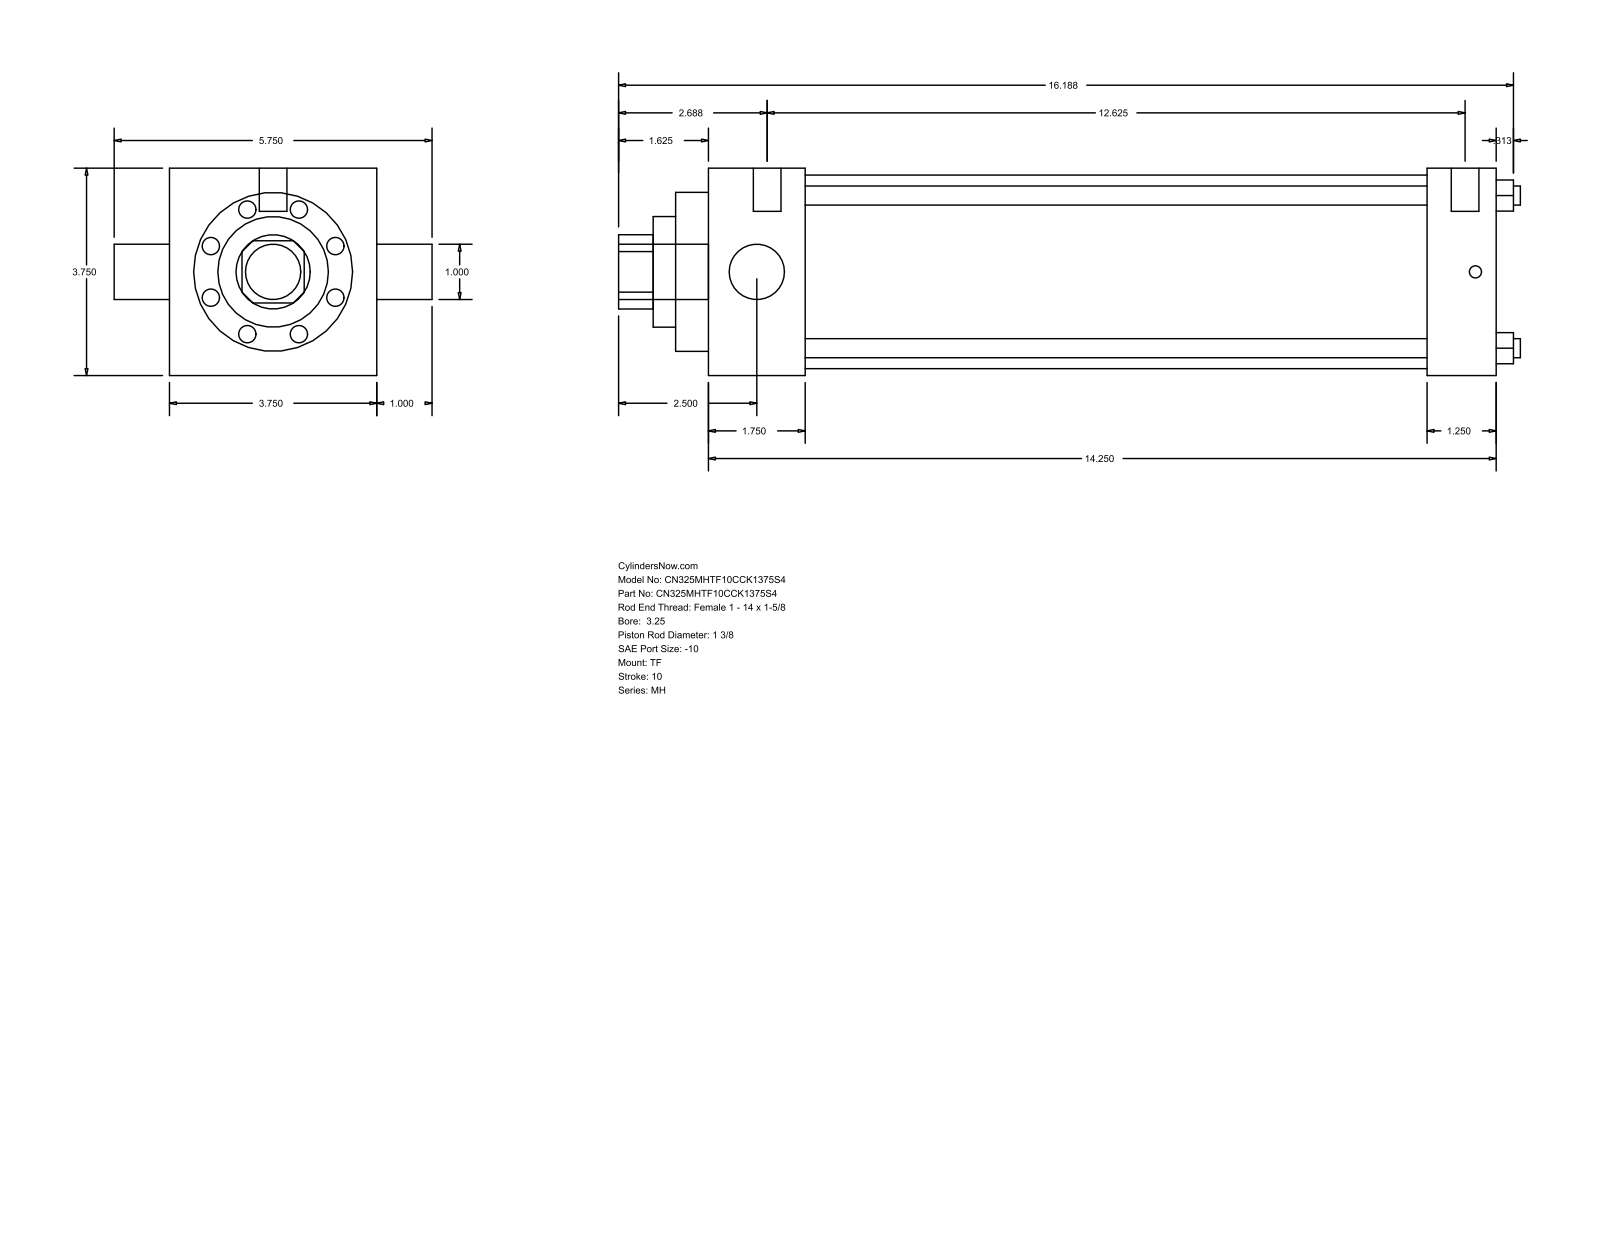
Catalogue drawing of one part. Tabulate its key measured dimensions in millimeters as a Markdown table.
| quantity | value |
| --- | --- |
| part name | MH_TF__0325_1.375 |
| STEP written by | GSSL Pune (CONFIG_CONTROL_DESIGN) |
| units | millimeters |
| bodies | 0 solids, 86 faces (61 planar, 25 cylindrical, 0 other) |
| overall size | 414.34 × 146.05 × 95.25 |
| round holes (diameter × count) | 8.76 × 4, 25.4 × 1, 34.92 × 1, 50.8 × 1, 73.03 × 1, 88.9 × 1 |
| round bosses / shafts (diameter × count) | 5.56 × 3, 12.7 × 2, 25.4 × 1 |
| partial cylindrical surfaces (radius × count) | 17.06 × 1 |
| main face-to-face distances | 95.24, 361.96, 44.45, 330.21, 285.76, 317.51, 31.75, 15.08, 59.53, 345.29 |
| hole center spacings | 49.57, 70.1, 99.14 |
